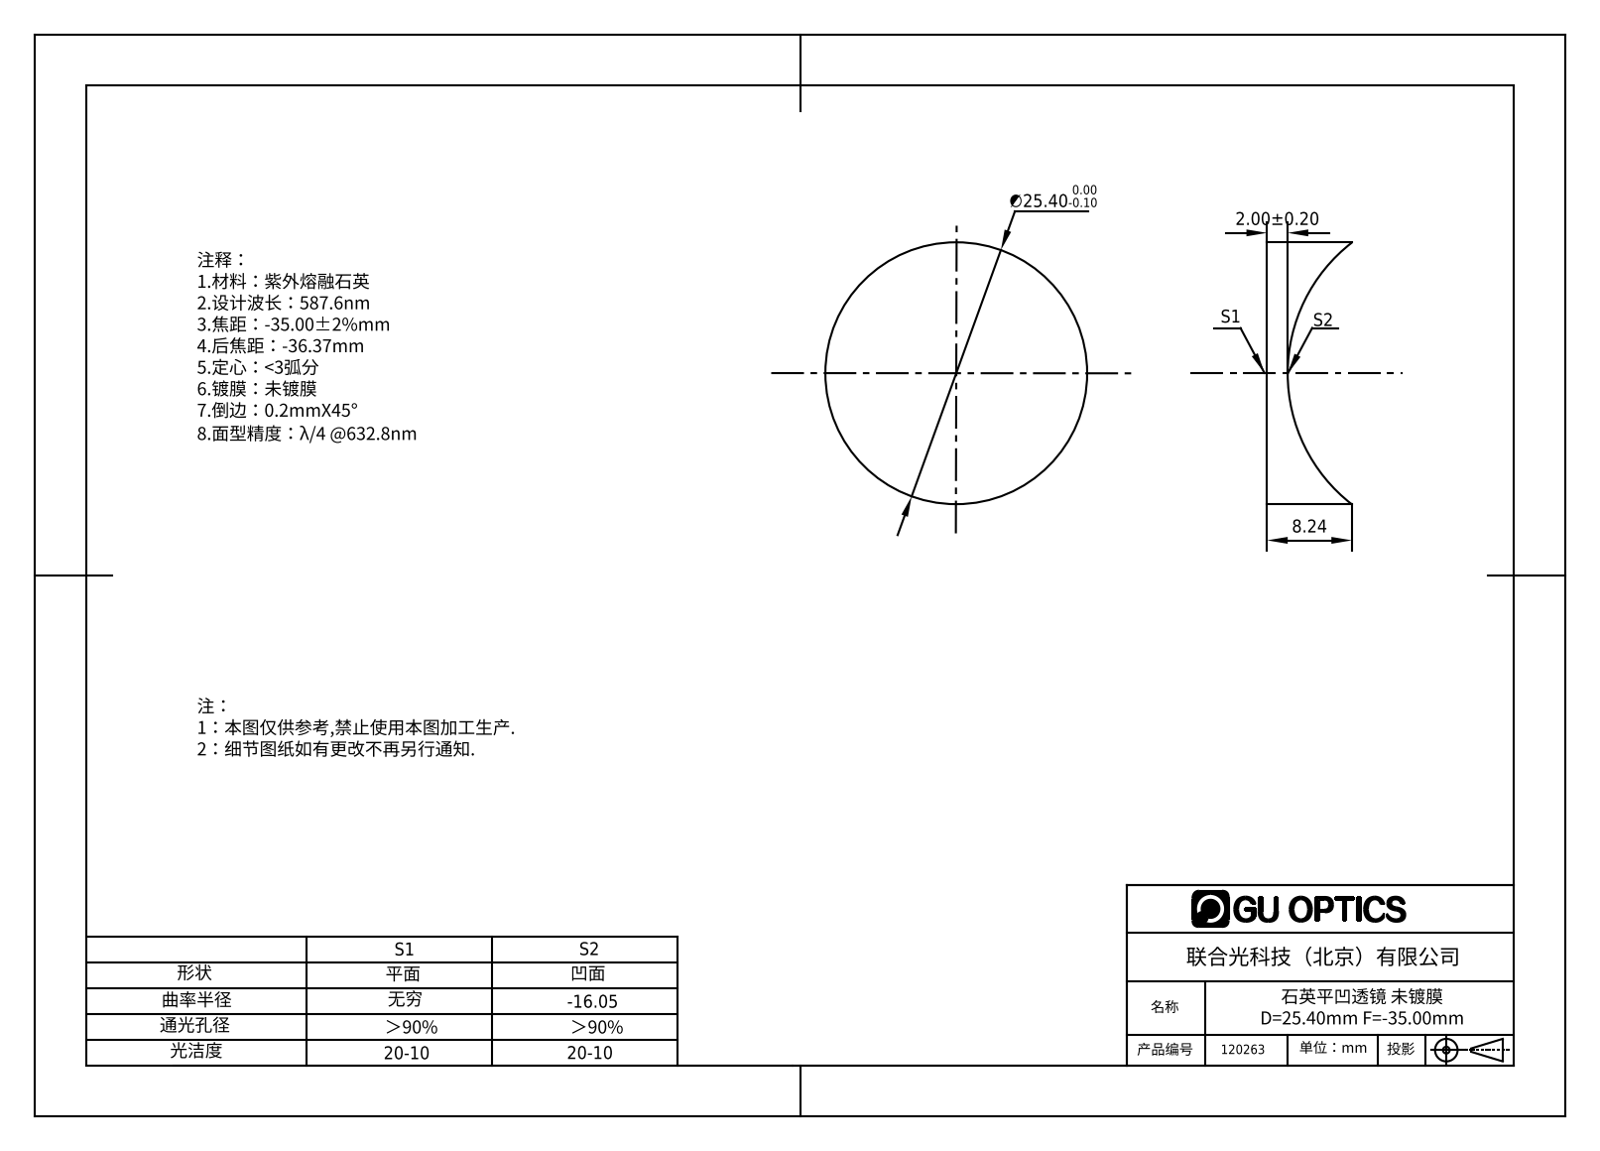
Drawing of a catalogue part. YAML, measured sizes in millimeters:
part_name: "120263"
step_written_by: "SolidWorks 2016 (AUTOMOTIVE_DESIGN)"
units: millimeters
bodies: {solids: 1, faces: 5, planar: 1, cylindrical: 2, other: 2}
overall_size: [25.4, 25.4, 8.24]
volume: 2466
surface_area: 1793
round_bosses_or_shafts:
  - {diameter: 25.4, count: 1}
